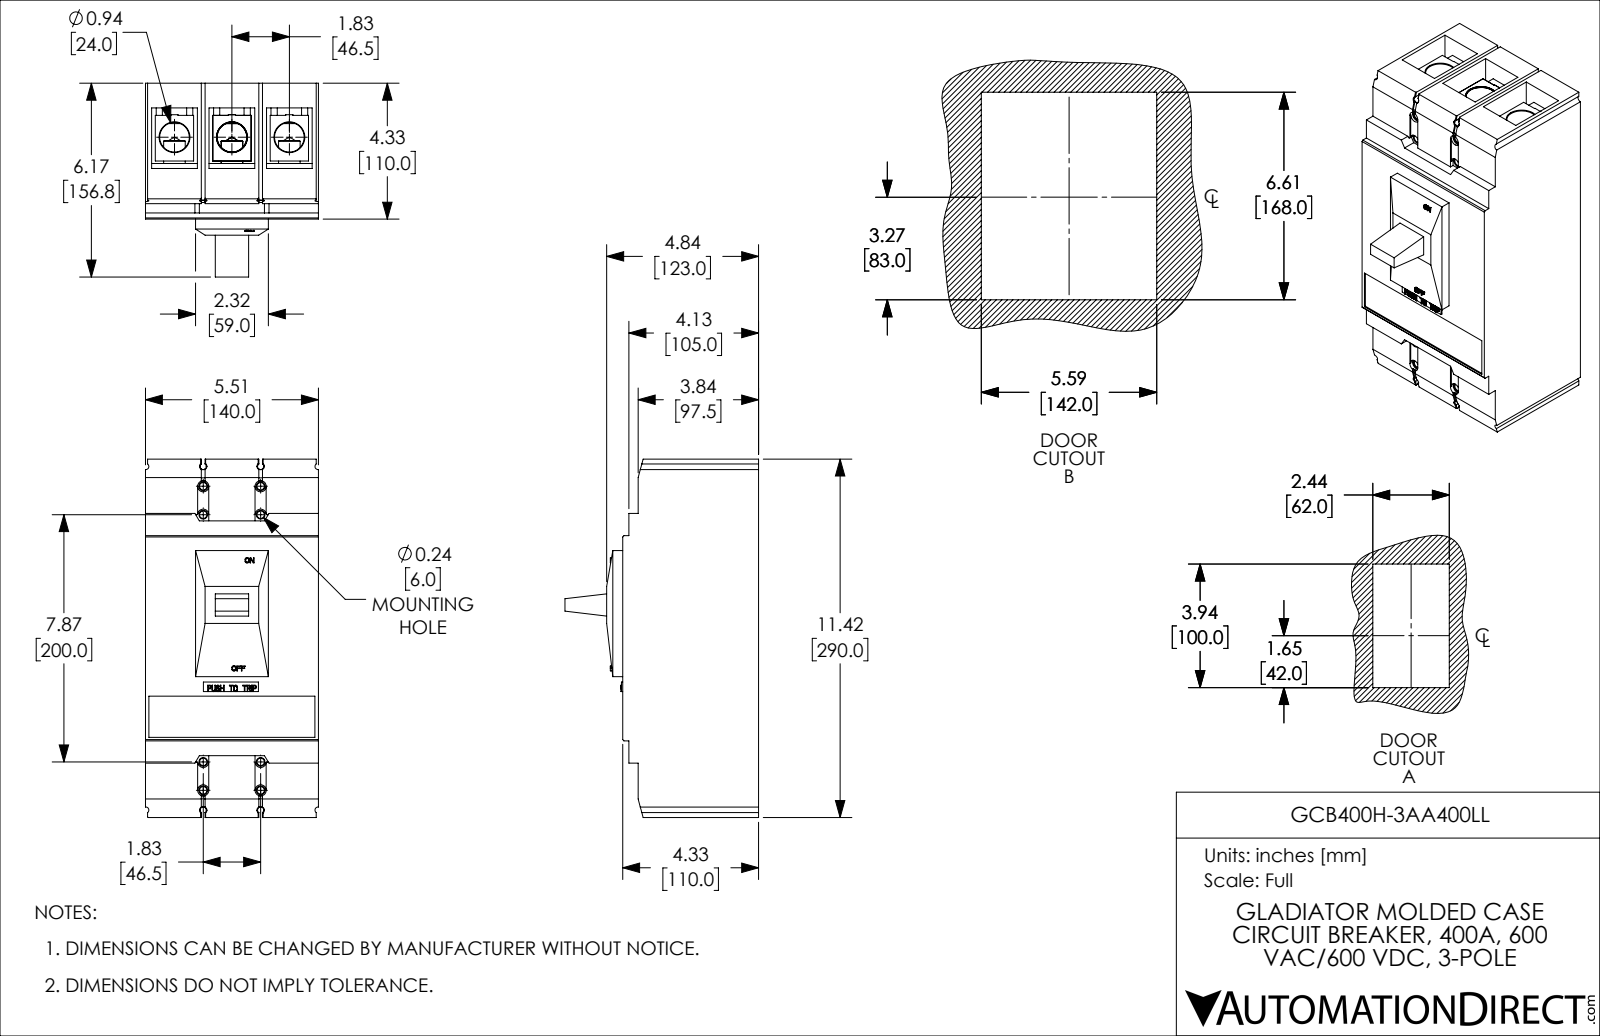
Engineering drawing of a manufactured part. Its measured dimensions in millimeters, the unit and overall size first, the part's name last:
Units: millimetres
Overall size (bounding box): 290 × 156.8 × 140
Round holes (diameter × count): ⌀6 ×8, ⌀10.5 ×6, ⌀15.1 ×6, ⌀17.5 ×6, ⌀5 ×4, ⌀9 ×4, ⌀24 ×3
Round bosses / shafts (diameter × count): ⌀14.6 ×6, ⌀10 ×6, ⌀19.1 ×1
Partial cylindrical surfaces — rounded edges, fillets, slot ends (radius × count): R2.5 ×28, R1 ×8, R4.5 ×4
Main face-to-face distances: 46.5, 140, 12.5, 37, 3, 34, 45, 43.5, 49.5, 5
Hole centre spacings: 46.5, 24.6, 27.7, 33.4, 216.3, 239.1, 255.1, 16
Volume: 4 028 000 mm³ · Surface area: 339 200 mm²
Bodies: 26 solids, 1319 faces (935 planar, 200 cylindrical, 184 other)
Part name (STEP PRODUCT): GCB400H-3AA400LL
STEP written by: SolidWorks 2021 (CONFIG_CONTROL_DESIGN)
